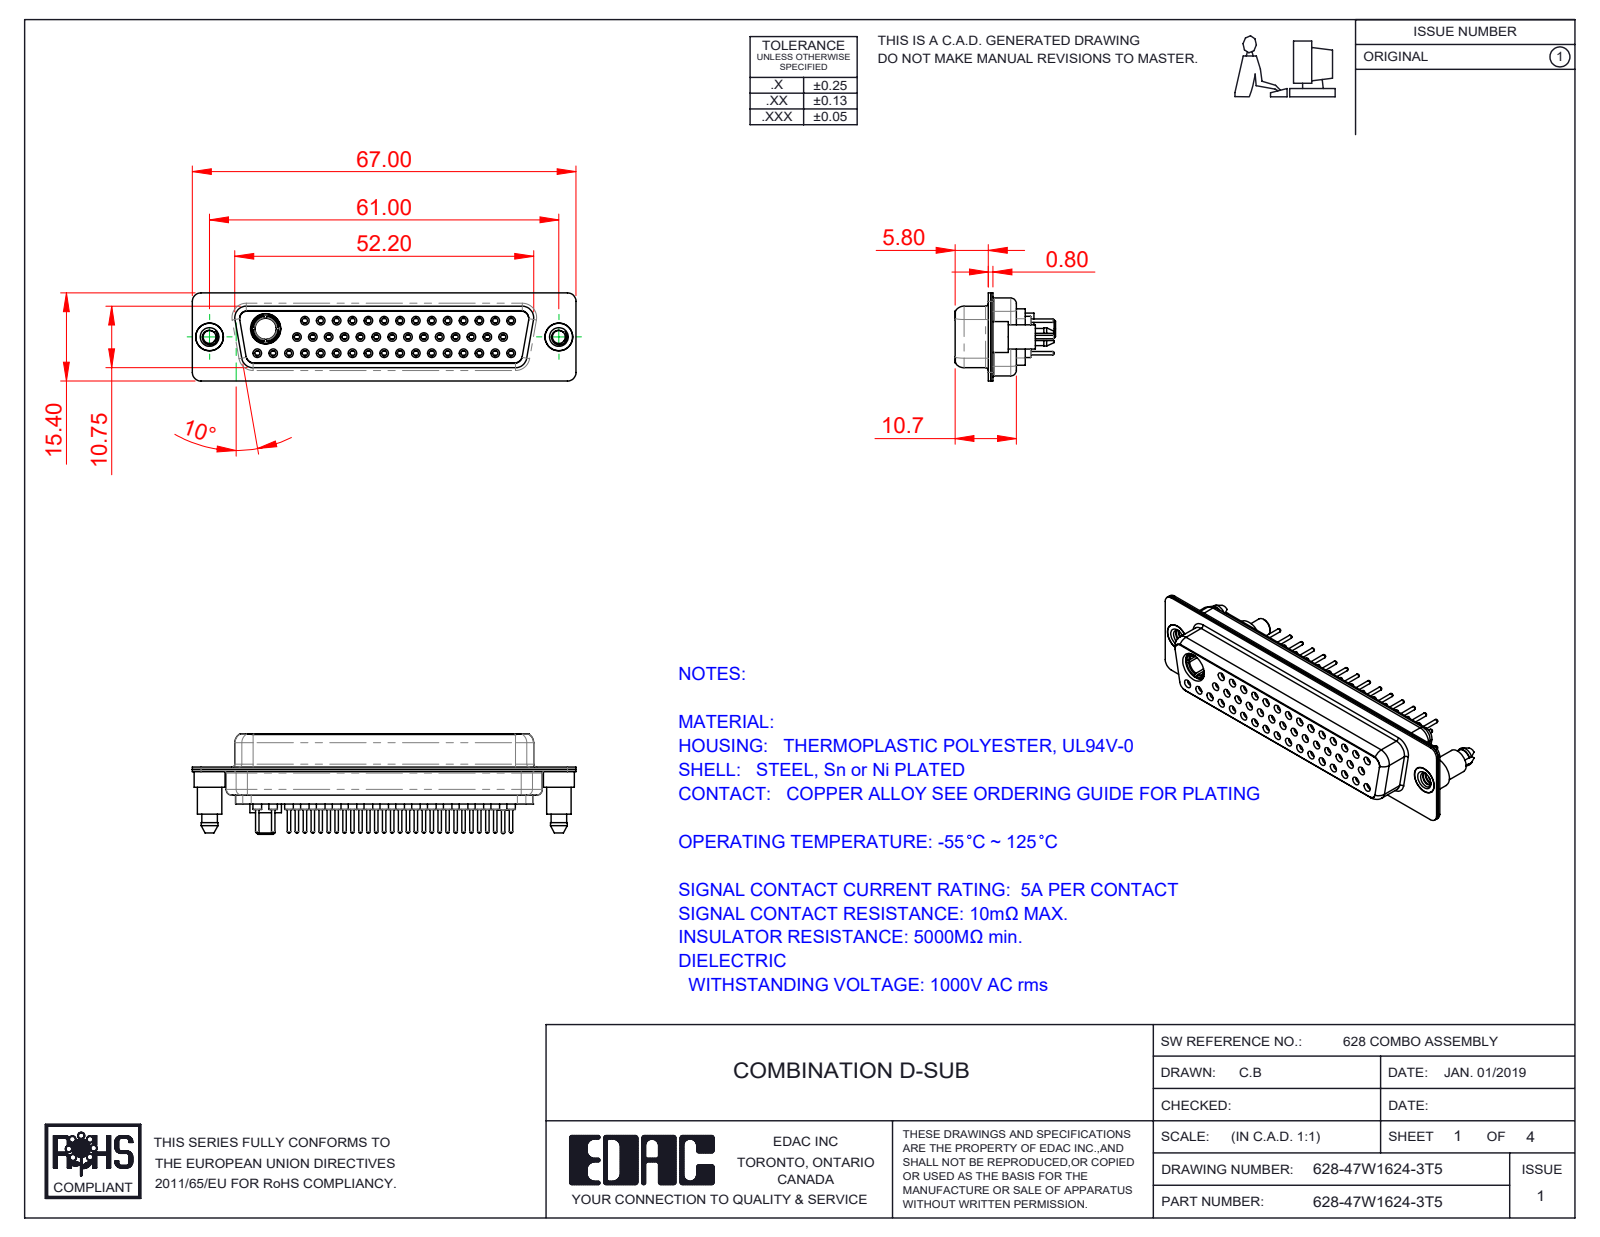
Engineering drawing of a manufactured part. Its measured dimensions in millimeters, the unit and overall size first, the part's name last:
Units: millimetres
Overall size (bounding box): 67 × 17.55 × 15.4
Round holes (diameter × count): ⌀1.1 ×46, ⌀0.9 ×45, ⌀1.5 ×45, ⌀2 ×45, ⌀1.6 ×31, ⌀1.7 ×14, ⌀4.85 ×3, ⌀2.26 ×2, ⌀4 ×2, ⌀4.05 ×2, ⌀3.7 ×1, ⌀5.3 ×1
Round bosses / shafts (diameter × count): ⌀2.2 ×46, ⌀0.6 ×46, ⌀1.6 ×15, ⌀5.4 ×2, ⌀4.95 ×2, ⌀4.8 ×2, ⌀4.25 ×2, ⌀5.5 ×1
Partial cylindrical surfaces — rounded edges, fillets, slot ends (radius × count): R1.5 ×18, R1.35 ×12, R2 ×12, R1.6 ×10, R0.25 ×4, R0.5 ×4, R0.6 ×4, R0.65 ×4
Main face-to-face distances: 0.4, 11.33, 6.45, 6.05, 1.87, 12.25, 6.2, 5.8, 10.35, 10.93
Hole centre spacings: 3.16, 2.77, 5.54, 8.31, 11.08, 13.85, 16.62, 19.39
Volume: 7 227 mm³ · Surface area: 15 028 mm²
Bodies: 53 solids, 2921 faces (799 planar, 1058 cylindrical, 1064 other)
Part name (STEP PRODUCT): 628Combo Contact Row 2_24; Power Socket_30A S; 628Combo Housing_47W1; 628Combo Shell Rear_50 Contacts (+5 more)
STEP written by: SolidWorks 2016 (CONFIG_CONTROL_DESIGN)
